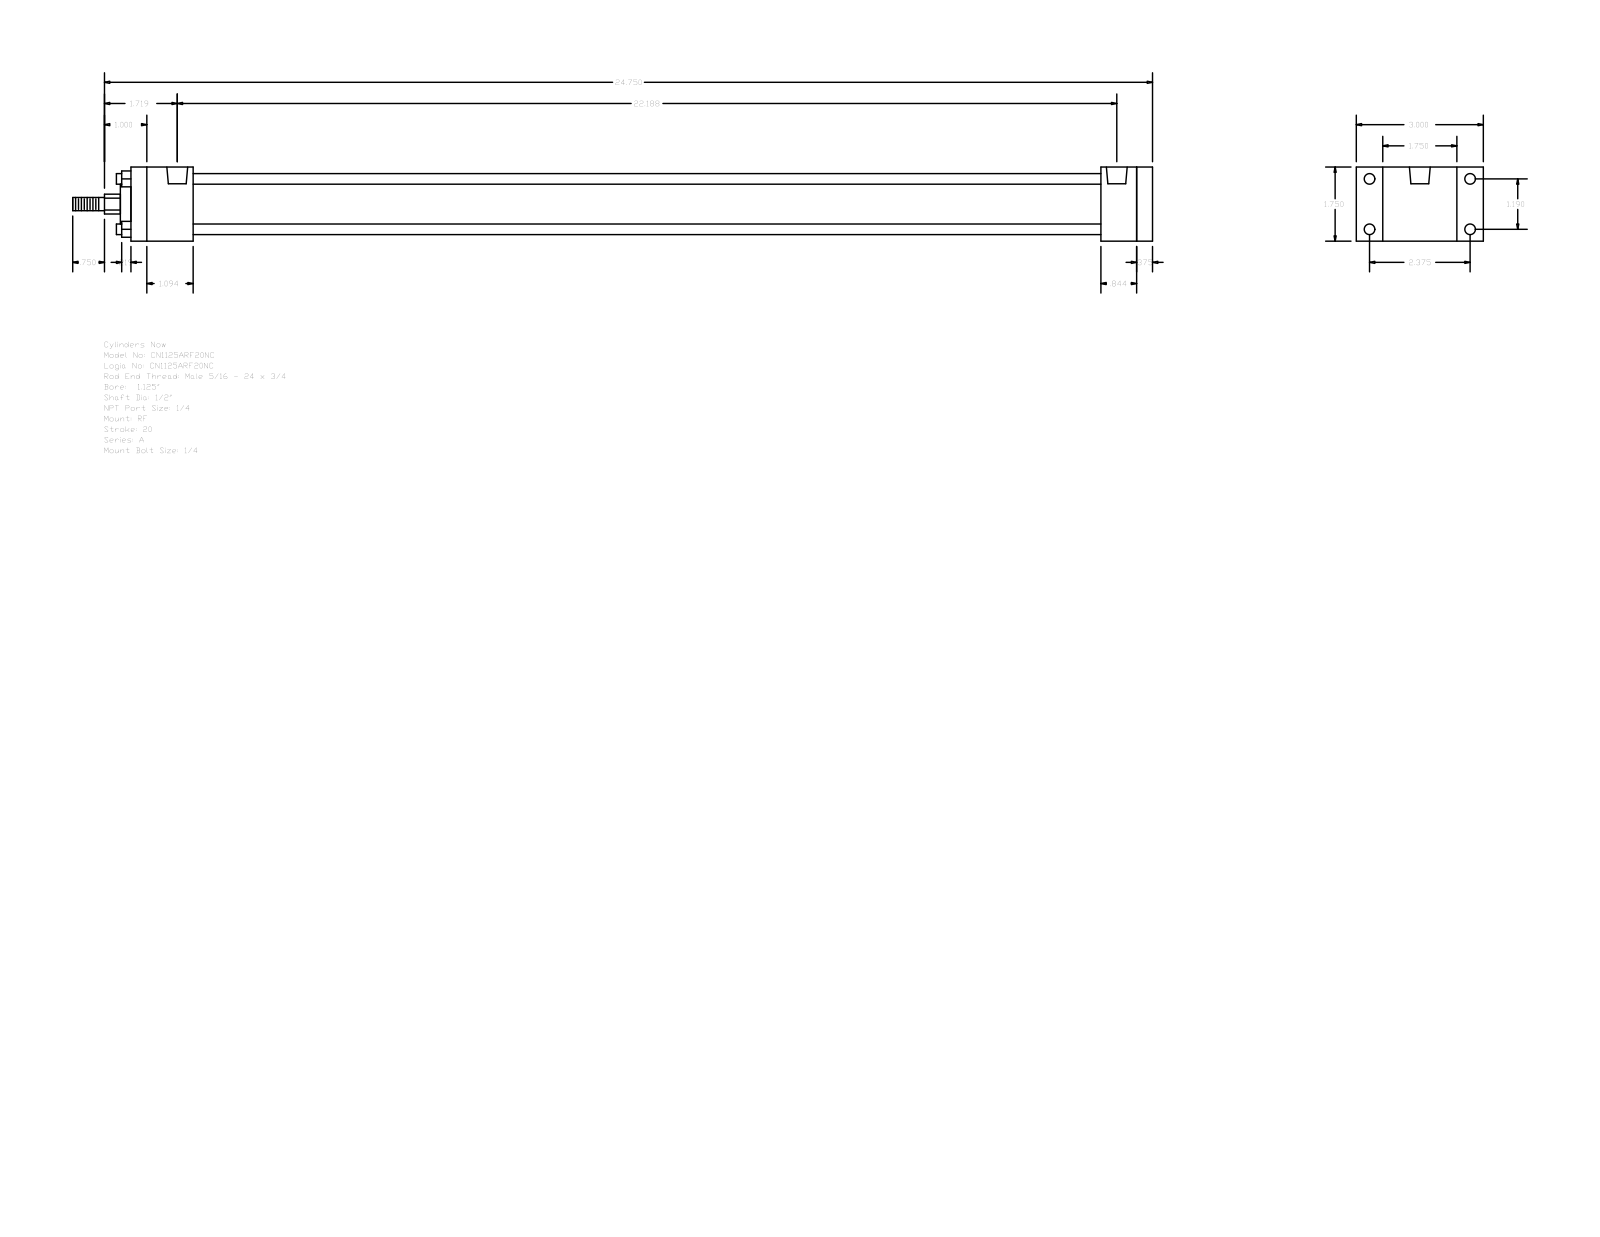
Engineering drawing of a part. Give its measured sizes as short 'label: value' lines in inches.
name: A_RF__0112_0.5
written by: GSSL Pune (CONFIG_CONTROL_DESIGN)
unit: in
bodies: 0 solids, 92 faces (64 planar, 28 cylindrical, 0 other)
size: 25.5 × 3 × 1.75
holes: 4× ⌀0.219, 4× ⌀0.25, 2× ⌀0.492
bosses: 4× ⌀0.25, 1× ⌀1.255, 1× ⌀0.937, 1× ⌀0.5, 1× ⌀0.313
rounds: 1× R0.234
face distances: 1.75, 0.375, 24.125, 23.75, 1.469, 22.906, 21.437, 22.281, 22.656, 0.844
hole spacings: 1.19, 2.375, 2.656, 22.063, 0.062, 0.063, 22.125, 22.125
